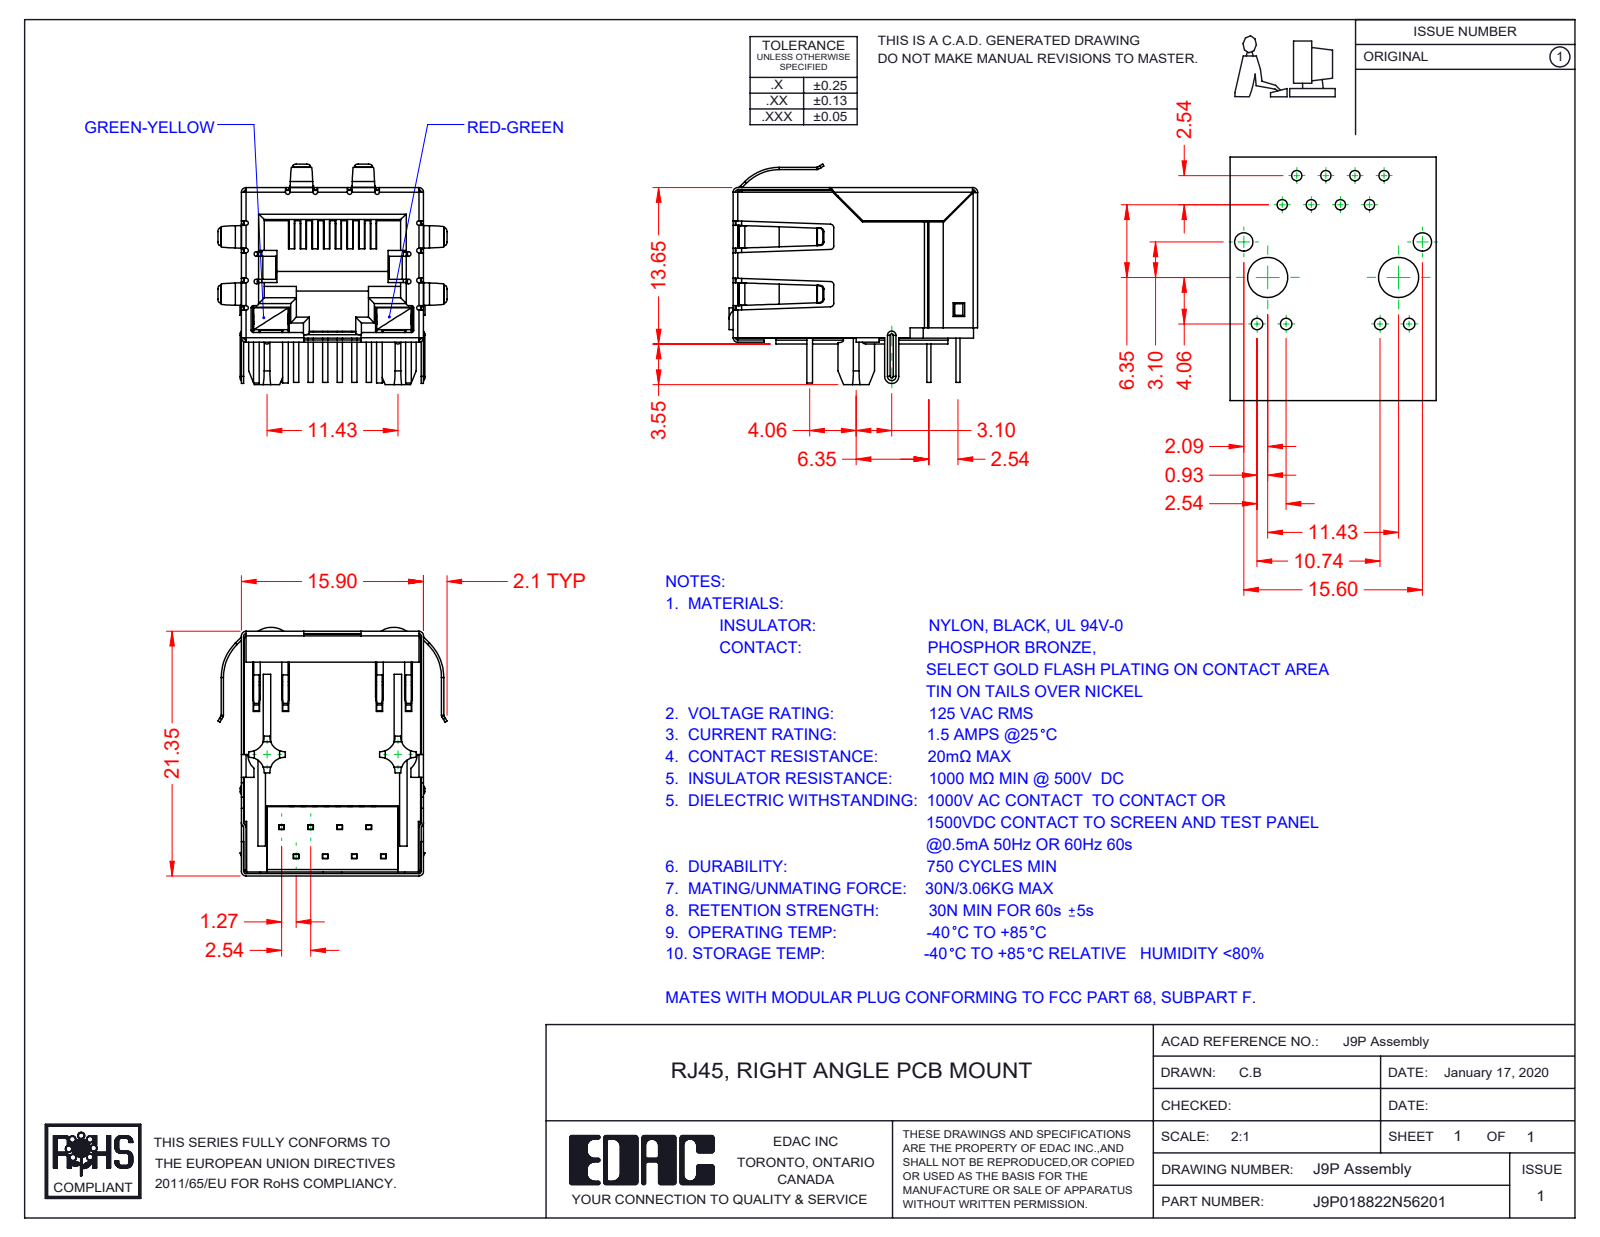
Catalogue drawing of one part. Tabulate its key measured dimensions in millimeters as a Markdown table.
| quantity | value |
| --- | --- |
| part name | 9P-LED Insulator; 9P-LED Contact Lock; 9P-LED LED RH_6-Red-Green; J9P018822N56202 (+4 more) |
| STEP written by | SolidWorks 2016 (CONFIG_CONTROL_DESIGN) |
| units | millimeters |
| bodies | 13 solids, 1476 faces (1042 planar, 340 cylindrical, 94 other) |
| overall size | 21.7 × 20 × 19.25 |
| volume | 2 687 mm³ |
| surface area | 7 515 mm² |
| partial cylindrical surfaces (radius × count) | 0.2 × 39, 0.5 × 22, 0.3 × 20, 0.4 × 16, 1.3 × 8, 0.23 × 5, 0.11 × 4, 0.31 × 4 |
| main face-to-face distances | 15.45, 15.7, 15.65, 0.35, 0.54, 15.5, 12.36, 0.6, 1.4, 0.59 |
